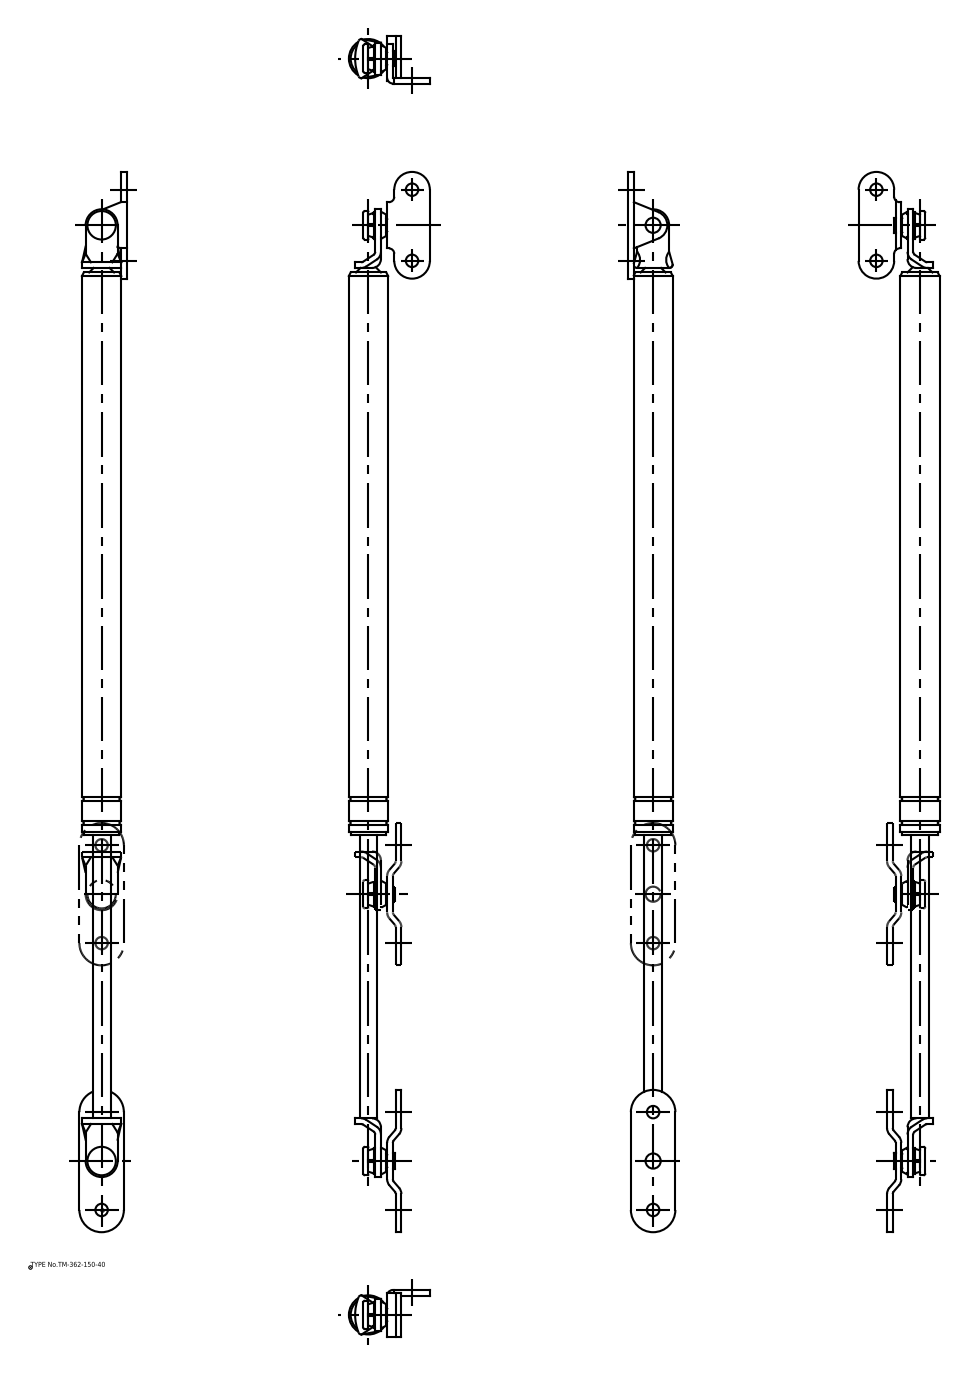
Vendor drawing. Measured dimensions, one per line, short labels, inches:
name: ブッシュ; ブラケット(A); ブラケット(B); ボルト (+2 more)
written by: spGate 16.7.1 (AUTOMOTIVE_DESIGN)
unit: in
bodies: 8 solids, 225 faces (113 planar, 84 cylindrical, 28 other)
size: 23.465 × 1.801 × 1.043
volume: 9.252 in³; area: 67.37 in²
holes: 4× ⌀0.276, 2× ⌀0.335
bosses: 3× ⌀0.394, 2× ⌀0.63, 2× ⌀0.591, 2× ⌀0.512, 1× ⌀0.886, 1× ⌀0.866, 1× ⌀0.787
rounds: 4× R0.079, 4× R0.205, 2× R0.02, 2× R0.173, 2× R0.197, 2× R0.354, 2× R0.394, 2× R0.492
face distances: 0.126, 0.453, 0.264, 0.189, 0.579, 0.138, 0.327, 0.315, 0.39, 0.063
hole spacings: 1.083, 1.575, 2.165, 19.626, 20.709, 21.791
